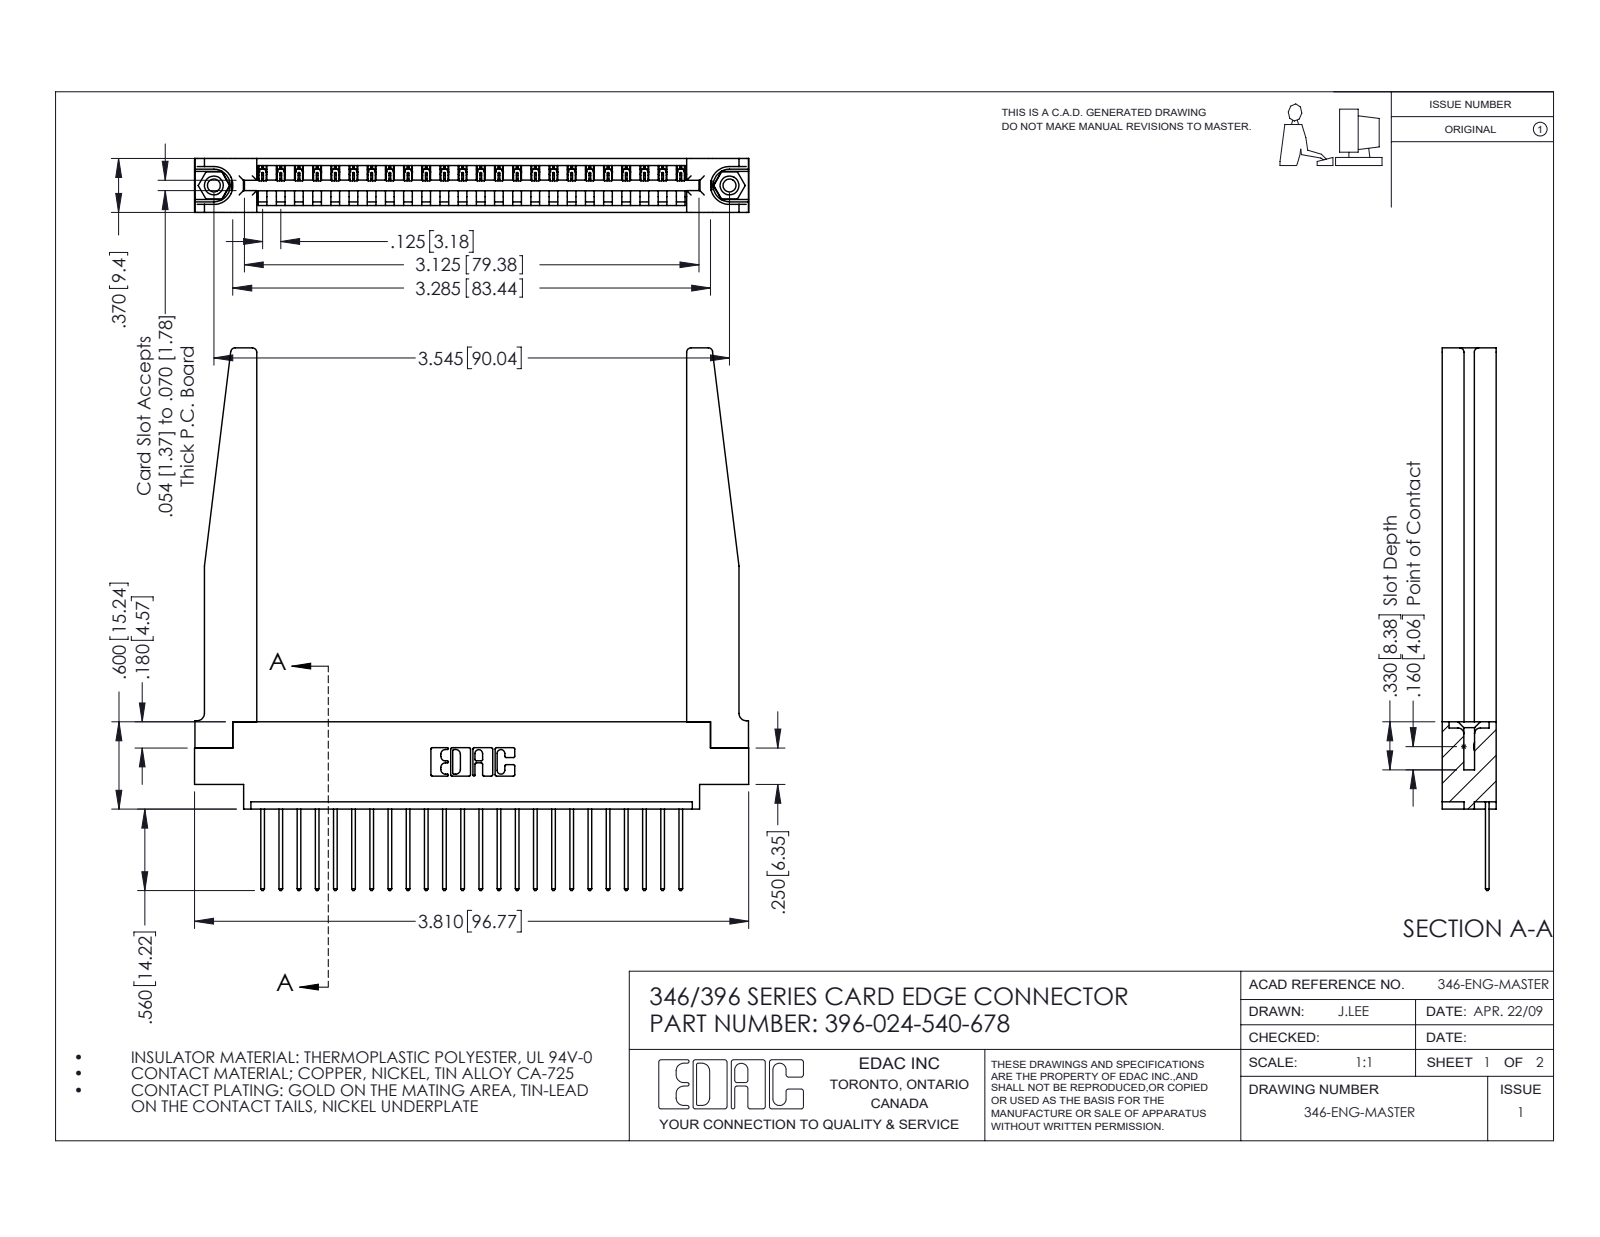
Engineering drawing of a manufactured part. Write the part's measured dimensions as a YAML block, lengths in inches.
part_name: "346-220-078_345-220-078; 345-292-001_345-293-140; 345-250-001_345-250-001-102; 396-024-540-678 (+1 more)"
step_written_by: "SolidWorks 2016 (CONFIG_CONTROL_DESIGN)"
units: inches
bodies: {solids: 29, faces: 1752, planar: 1182, cylindrical: 518, other: 52}
overall_size: [3.81, 3.73, 0.37]
volume: 0.972
surface_area: 27.92
round_holes:
  - {diameter: 0.089, count: 2}
  - {diameter: 0.125, count: 2}
  - {diameter: 0.156, count: 2}
  - {diameter: 0.064, count: 1}
round_bosses_or_shafts:
  - {diameter: 0.155, count: 2}
partial_cylinders:
  - {radius: 0.006, count: 48}
  - {radius: 0.01, count: 48}
  - {radius: 0.01, count: 22}
  - {radius: 0.03, count: 8}
  - {radius: 0.007, count: 6}
  - {radius: 0.031, count: 6}
  - {radius: 0.026, count: 3}
  - {radius: 0.031, count: 2}
face_to_face_distances: [0.37, 0.048, 0.322, 0.072, 0.148, 0.15, 0.25, 0.298, 0.025, 0.222]
hole_center_spacings: [0.246, 3.337, 3.545]
